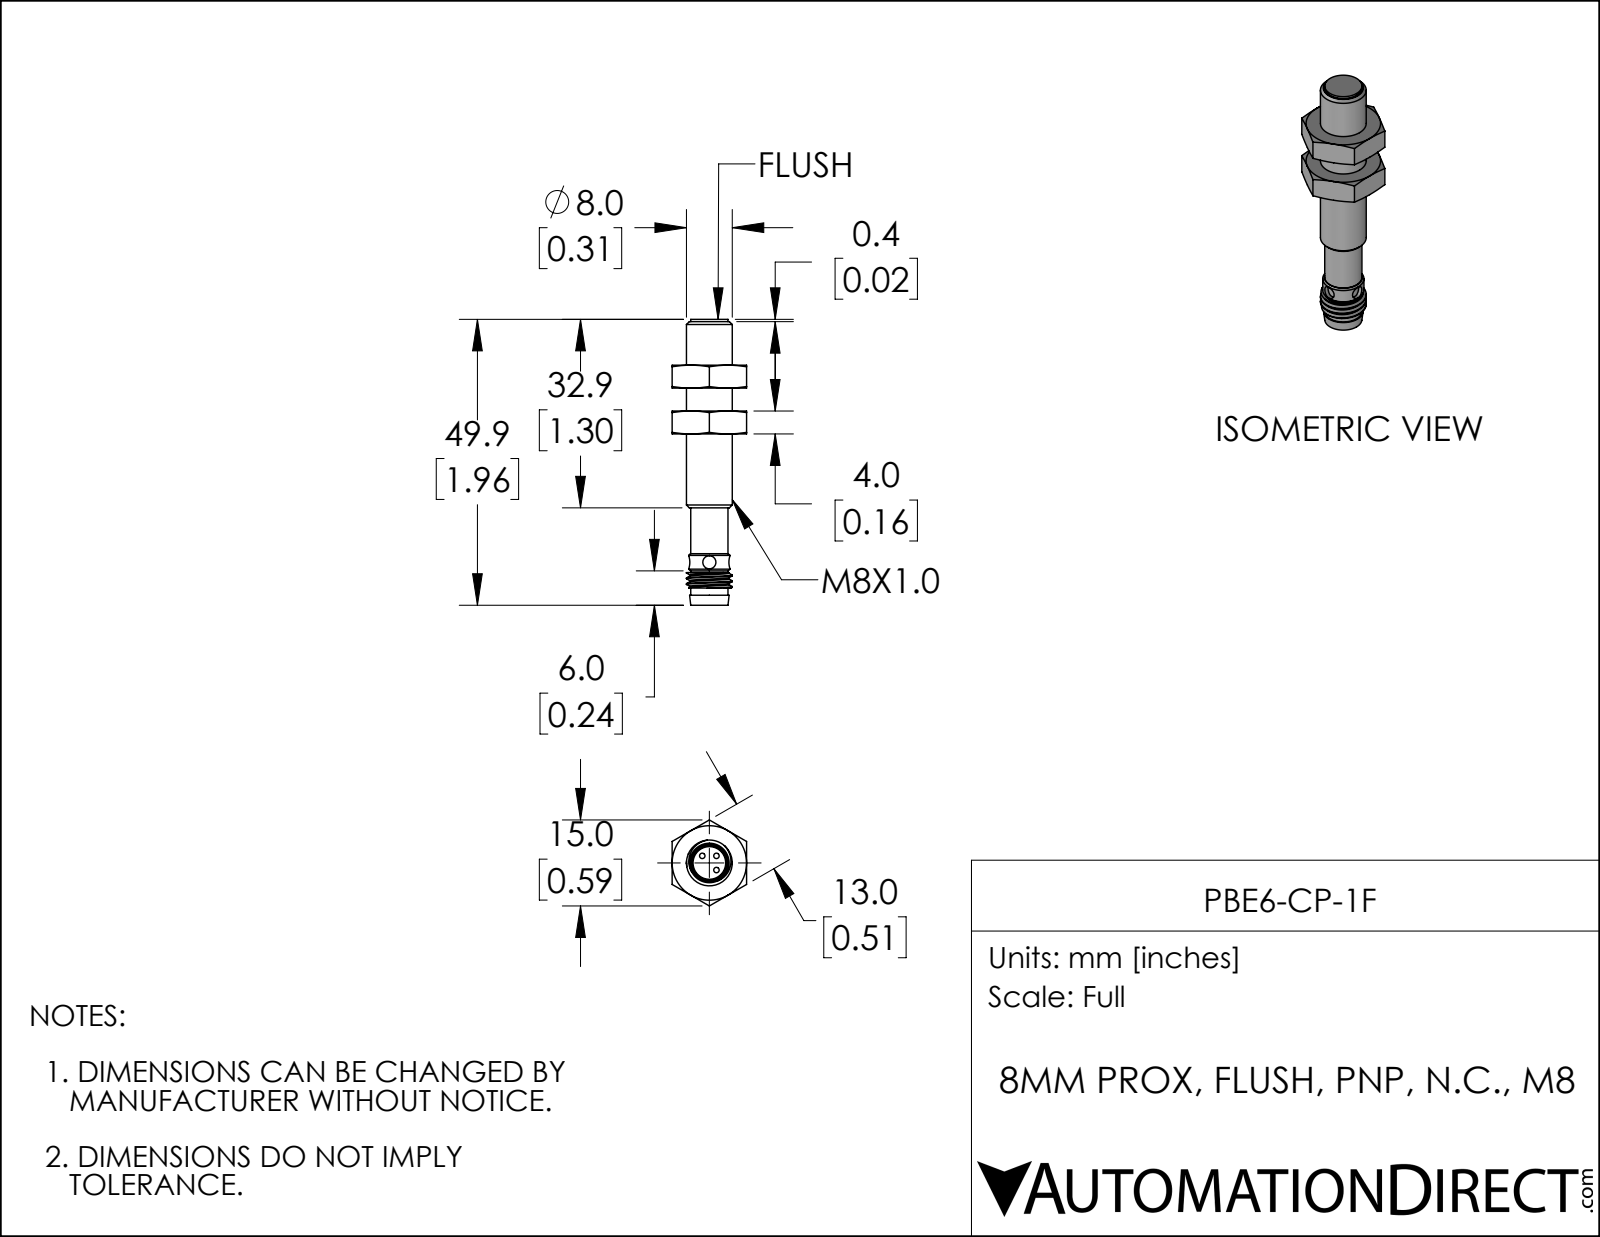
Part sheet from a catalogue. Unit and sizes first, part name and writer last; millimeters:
Units: millimetres
Overall size (bounding box): 49.9 × 8 × 8
Round holes (diameter × count): ⌀2.3 ×2, ⌀5.7 ×1
Round bosses / shafts (diameter × count): ⌀0.9 ×3, ⌀8 ×1, ⌀7.2 ×1, ⌀6.5 ×1
Partial cylindrical surfaces — rounded edges, fillets, slot ends (radius × count): R2.9 ×1
Main face-to-face distances: 44.9, 44.2, 0.7, 3, 49.9, 5.7, 5, 46.9, 2.7, 2
Volume: 2 130 mm³ · Surface area: 1 492 mm²
Bodies: 1 solid, 44 faces (10 planar, 22 cylindrical, 12 other)
Part name (STEP PRODUCT): DSD-0263-1
STEP written by: SolidWorks 2019 (AUTOMOTIVE_DESIGN)
